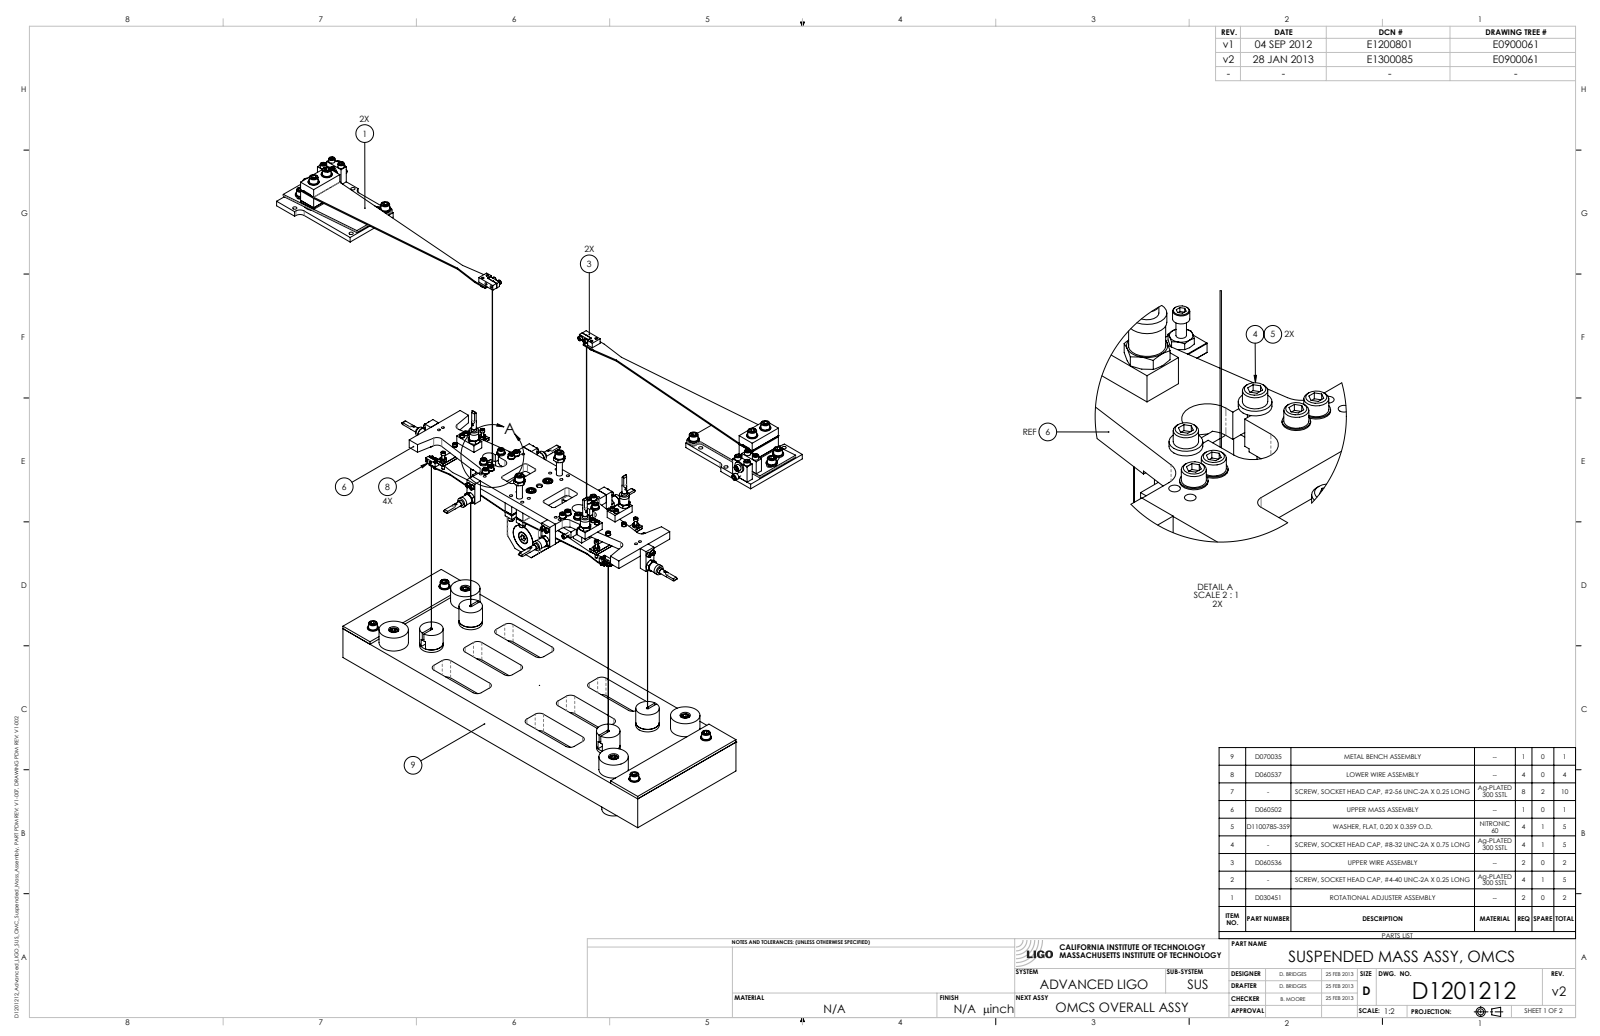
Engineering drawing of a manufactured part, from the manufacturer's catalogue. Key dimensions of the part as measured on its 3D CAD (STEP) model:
Part name (STEP PRODUCT): D030448_RotationalAdjuster_BasePlate; D080019_AdLIGO_OMC_LowerBlade; D1001697_Advanced_LIGO_SUS_HLTS_Magnet_Retainer,_BOSEM; D020350_100g_mass (+8 more)
STEP written by: SolidWorks 2013 (CONFIG_CONTROL_DESIGN)
Units: inches
Bodies: 366 solids, 6459 faces (2617 planar, 2552 cylindrical, 1290 other)
Overall size (bounding box): 28.967 × 22.121 × 6.841
Volume: 183.1 in³ · Surface area: 939.9 in²
Round holes (diameter × count): ⌀0.089 ×56, ⌀0.129 ×30, ⌀0.136 ×28, ⌀0.115 ×22, ⌀0.201 ×19, ⌀0.169 ×16, ⌀0.18 ×16, ⌀0.25 ×14, ⌀0.052 ×13, ⌀0.086 ×12, ⌀0.112 ×12, ⌀0.125 ×12
Round bosses / shafts (diameter × count): ⌀0.112 ×40, ⌀0.183 ×34, ⌀0.164 ×26, ⌀0.209 ×22, ⌀0.27 ×20, ⌀0.37 ×18, ⌀0.25 ×18, ⌀0.304 ×16
Partial cylindrical surfaces — rounded edges, fillets, slot ends (radius × count): R0.25 ×36, R0.125 ×26, R0.094 ×12, R0.063 ×10, R0.05 ×4, R0.09 ×4, R0.13 ×4, R0.133 ×4
Main face-to-face distances: 1.5, 0.394, 8.369, 20.098, 18.598, 11.493, 9.993, 8.605, 5.906, 10.387
Hole centre spacings: 0.12, 0.596, 0.607, 0.642, 4.503, 0.553, 0.717, 0.752
